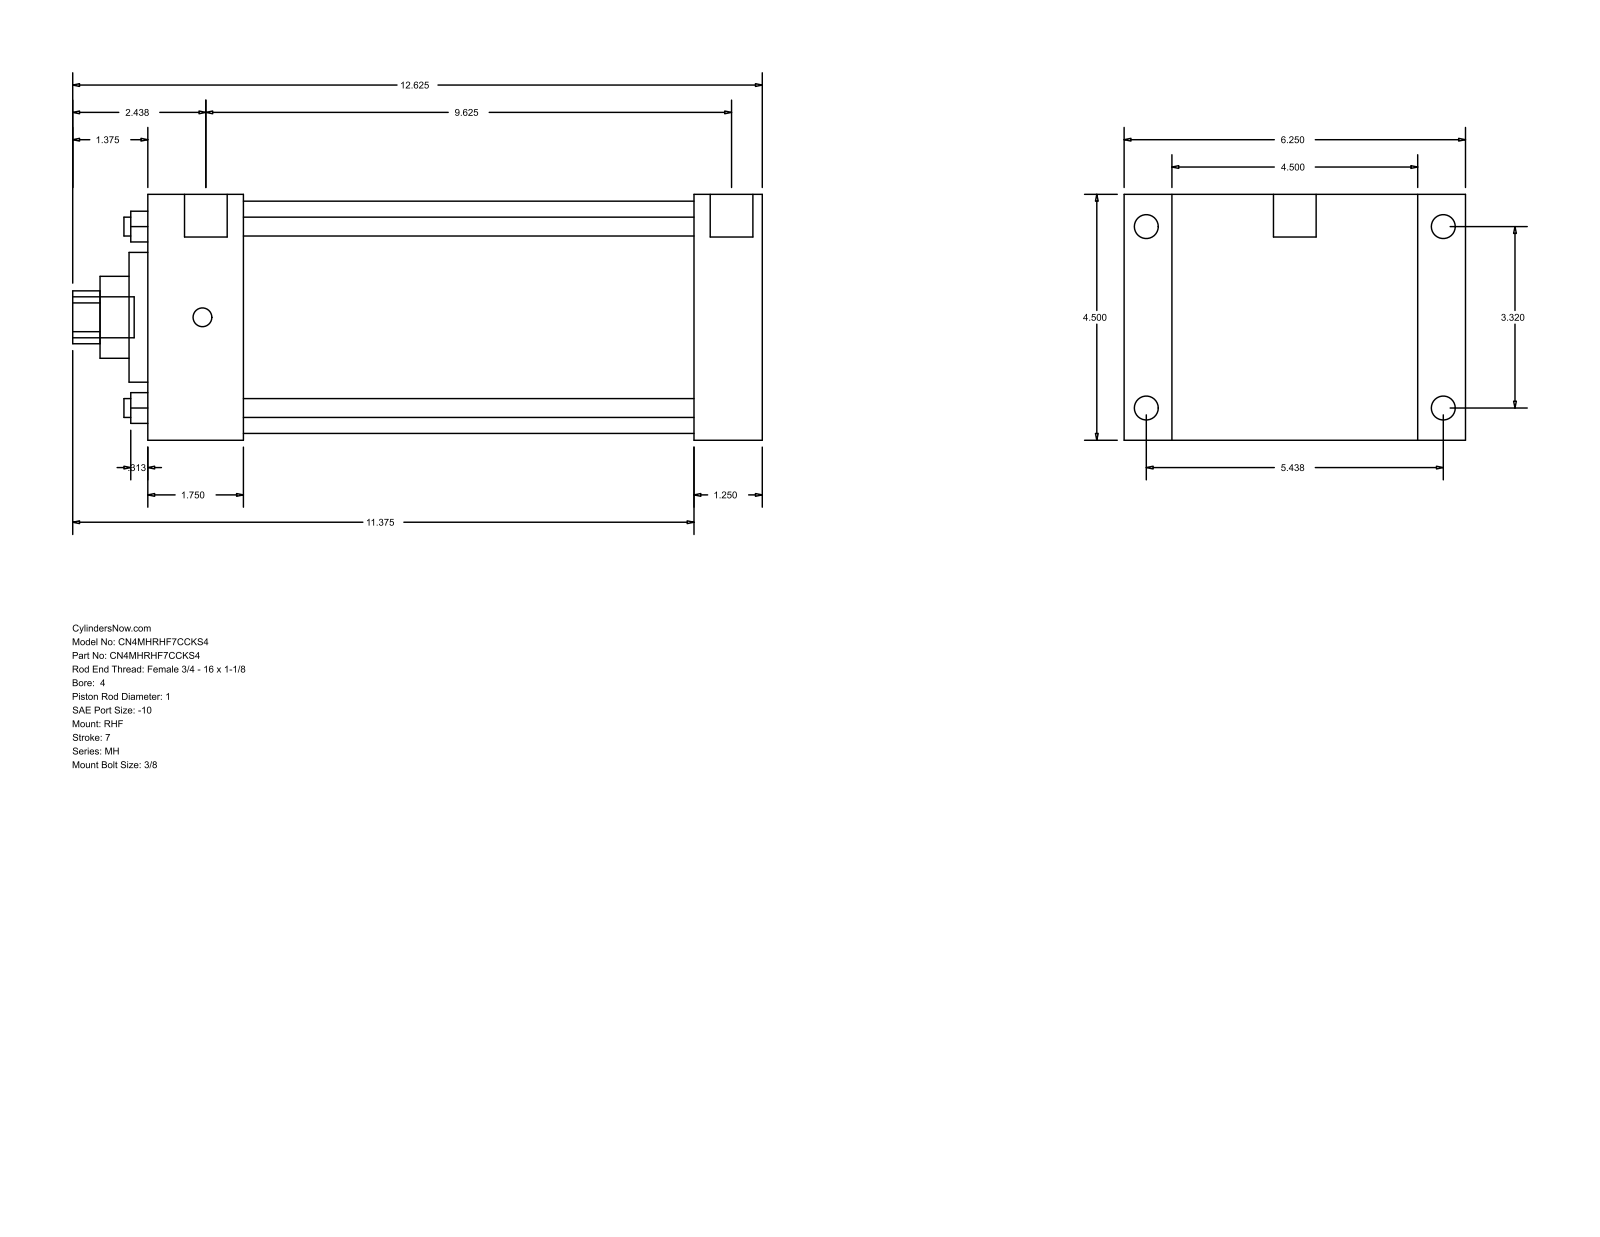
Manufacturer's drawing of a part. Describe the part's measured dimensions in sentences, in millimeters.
The part is named "MH_RHF__0400_1". Its 3-D file was written by "GSSL Pune (CONFIG_CONTROL_DESIGN)". It is 0 solids with 90 faces: 61 planar, 29 cylindrical and 0 other. Overall it measures 320.68 by 158.75 by 114.3 millimeters. Round holes: 4 of diameter 8.76, 1 of diameter 25.4, 1 of diameter 38.1, 1 of diameter 60.33, 1 of diameter 107.95. Round bosses or shafts: 4 of diameter 11.13, 4 of diameter 8.73, 2 of diameter 19.84, 1 of diameter 19.05. Partial cylindrical surfaces (rounded edges, fillets, slot ends): 1 of radius 12.29. The main face-to-face distances are 114.3, 285.76, 254.01, 31.75, 22.23, 136.53, 44.46, 209.55, 241.3, 158.76. The hole center spacings are 59.62, 84.32, 119.25.
